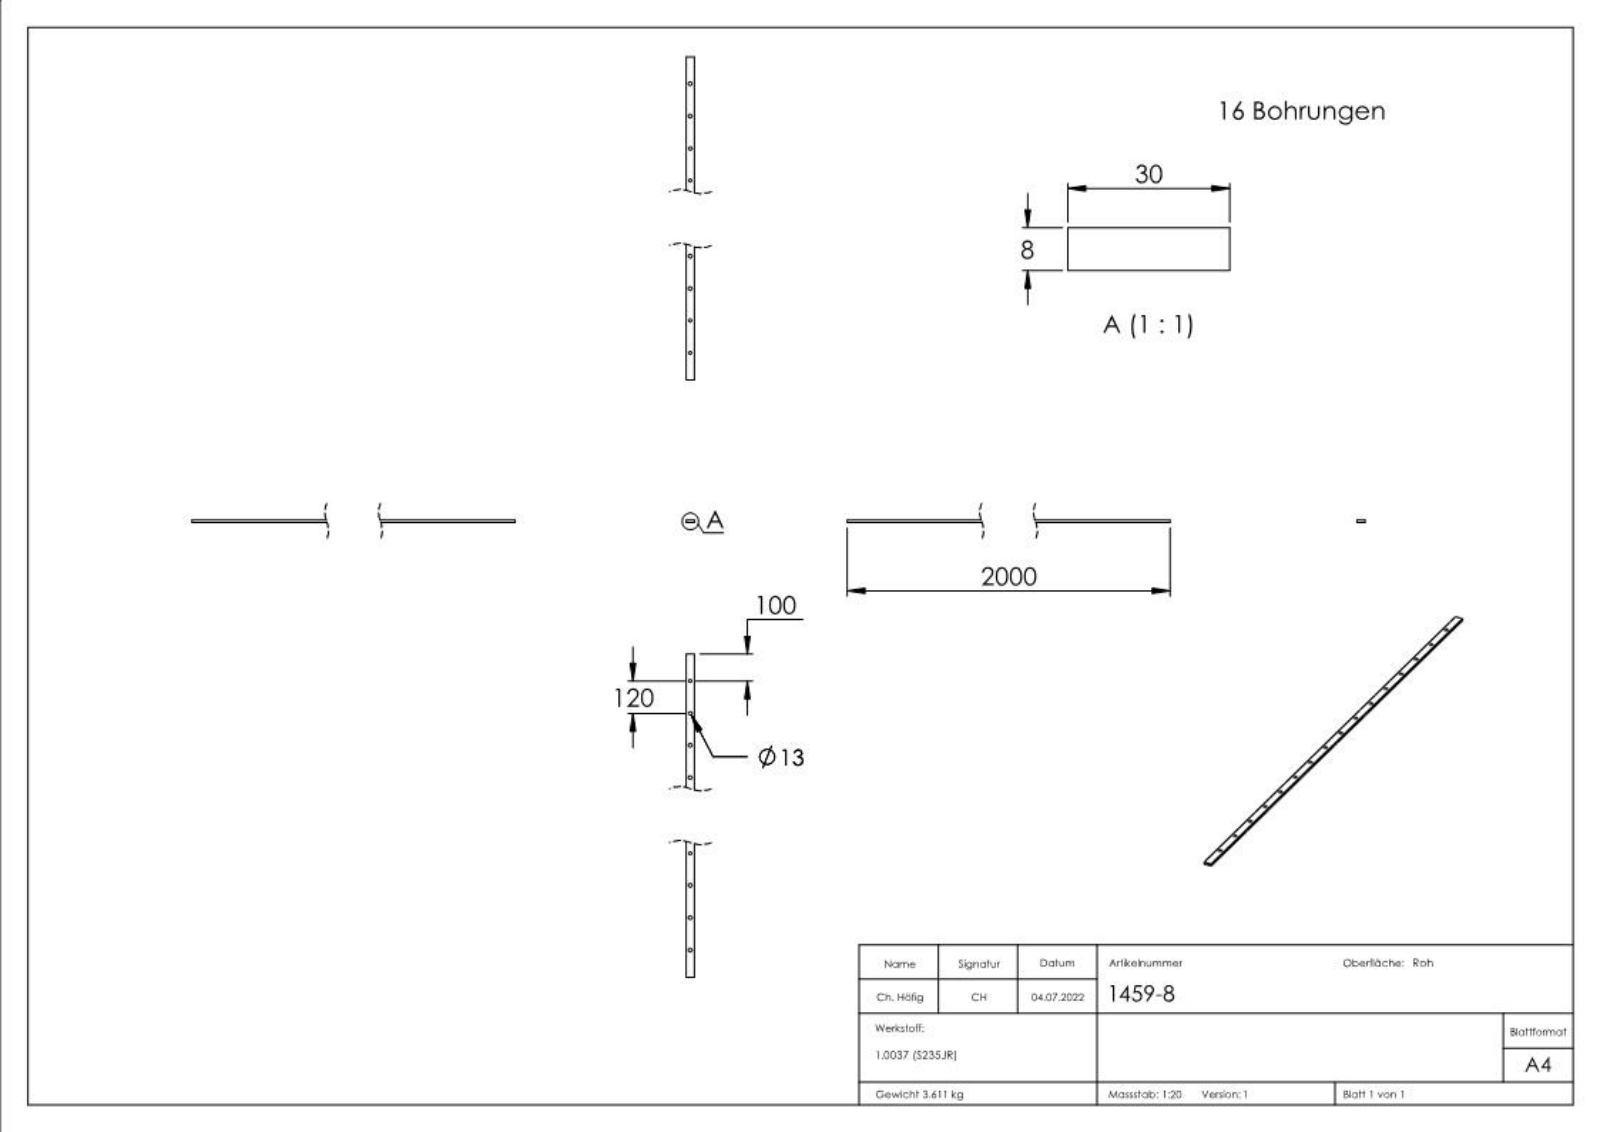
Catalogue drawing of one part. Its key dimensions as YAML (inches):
part_name: "1459-8"
step_written_by: "SolidWorks 2018 (CONFIG_CONTROL_DESIGN)"
units: inches
bodies: {solids: 1, faces: 254, planar: 136, cylindrical: 16, other: 102}
overall_size: [78.74, 1.181, 0.315]
volume: 28.25
surface_area: 237.9
round_holes:
  - {diameter: 0.512, count: 16}
face_to_face_distances: [0.315, 1.181, 78.74, 0.311, 0.045, 0.079, 0.044, 0.129, 0.05, 0.013]
hole_center_spacings: [4.724, 9.449, 14.173, 18.898, 23.622, 28.346, 33.071, 37.795]
